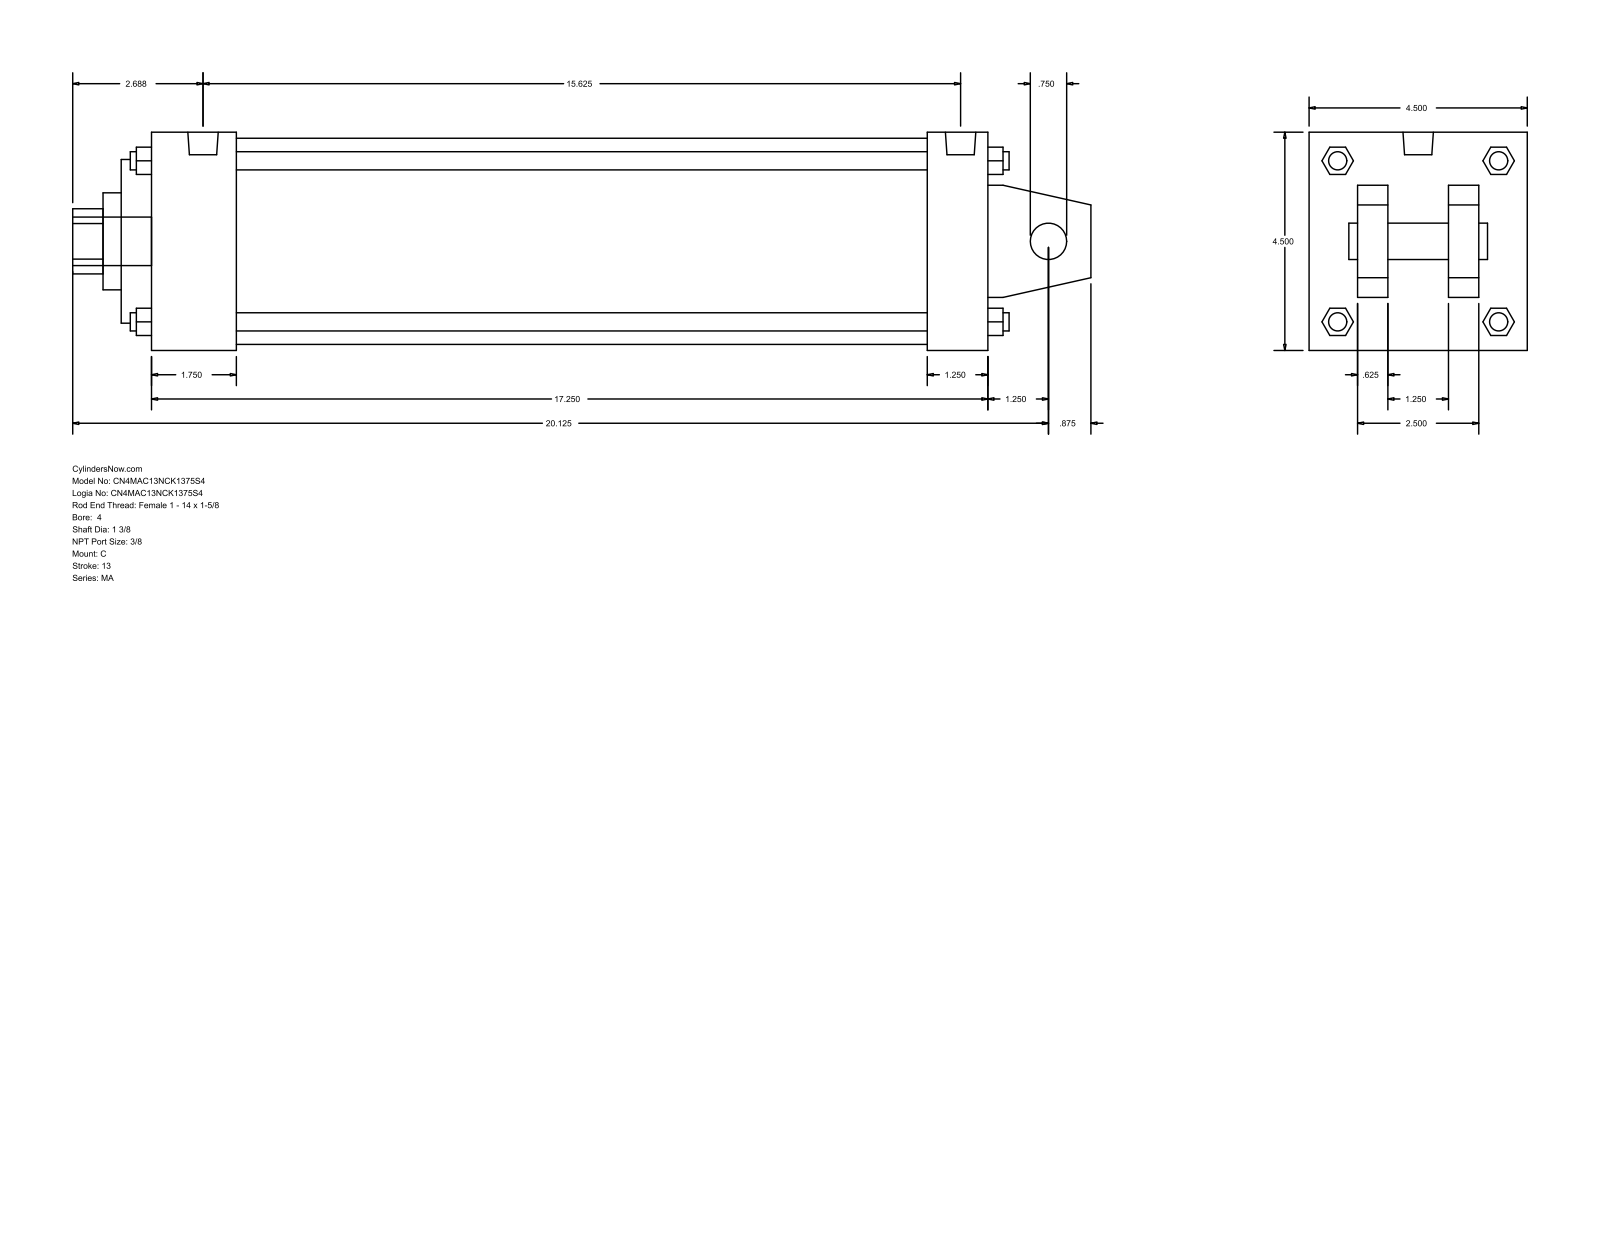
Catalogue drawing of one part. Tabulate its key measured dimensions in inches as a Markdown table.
| quantity | value |
| --- | --- |
| part name | MA_C__0400_1.375 |
| STEP written by | GSSL Pune (CONFIG_CONTROL_DESIGN) |
| units | inches |
| bodies | 0 solids, 141 faces (109 planar, 32 cylindrical, 0 other) |
| overall size | 21 × 4.5 × 4.5 |
| round holes (diameter × count) | 0.75 × 1, 1.375 × 1, 2 × 1, 3.375 × 1, 4.25 × 1 |
| round bosses / shafts (diameter × count) | 0.437 × 4, 0.375 × 4, 0.627 × 2, 1 × 1 |
| partial cylindrical surfaces (radius × count) | 0.672 × 1 |
| main face-to-face distances | 4.5, 0.625, 17.25, 2.875, 1.625, 1, 3.5, 1.875, 17.875, 16.625 |
